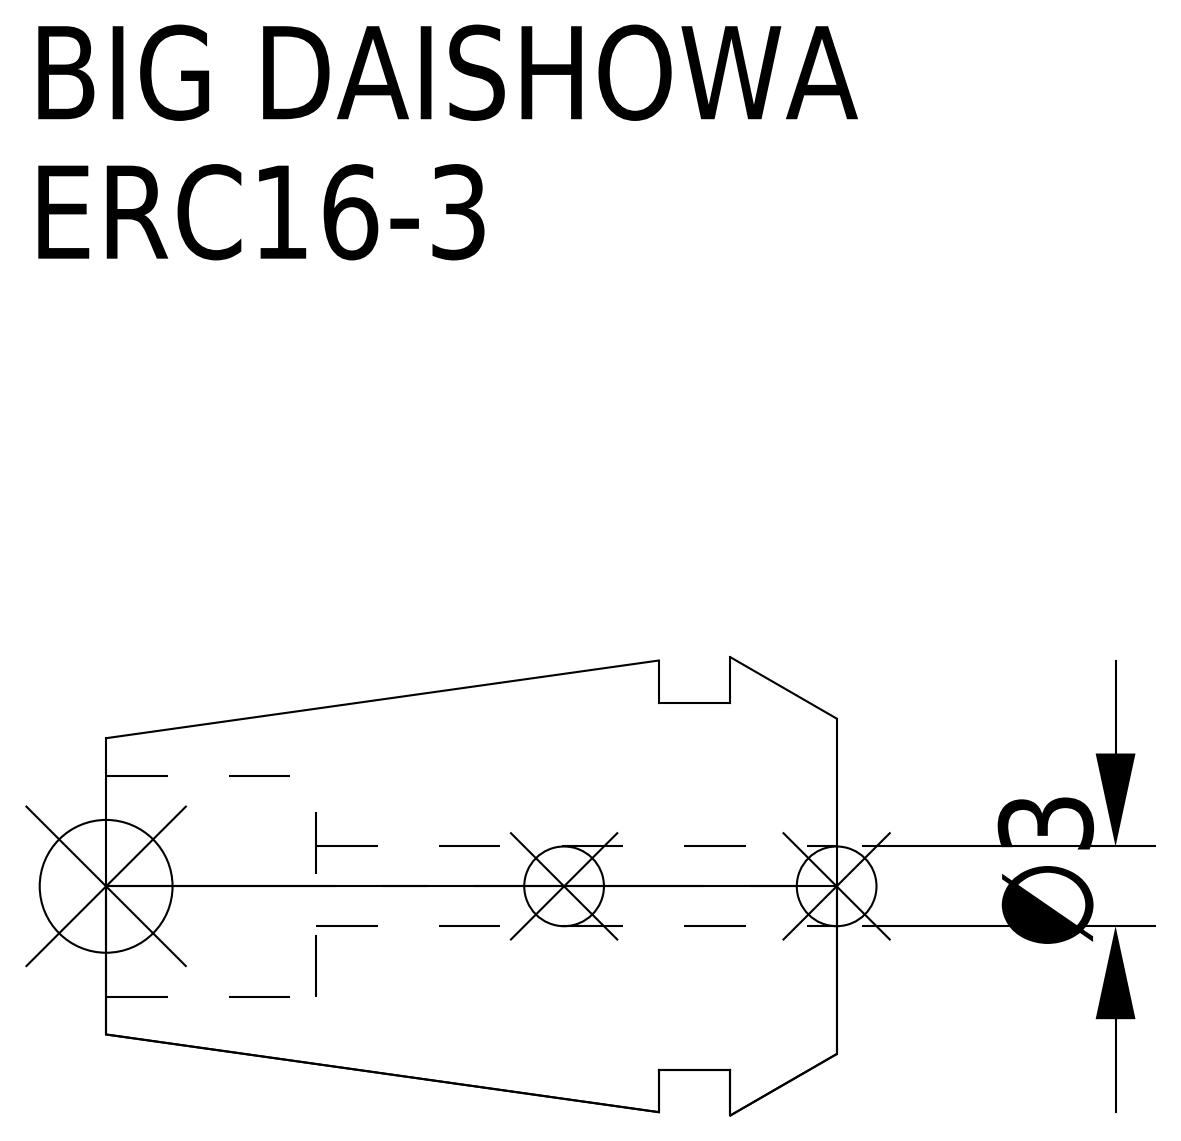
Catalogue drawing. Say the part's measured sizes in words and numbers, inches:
The part is named "ERC16-3". Its 3-D file was written by "CREO PARAMETRIC BY PTC INC, 2016380 (AUTOMOTIVE_DESIGN)". It is 1 solid with 15 faces: 5 planar, 6 cylindrical and 4 other. Overall it measures 1.083 by 0.679 by 0.679 inches. Its volume is 0.234 cubic inches and its surface area 3.137 square inches. Round holes: 1 of diameter 0.118, 1 of diameter 0.327. Round bosses or shafts: 1 of diameter 0.543. The main face-to-face distances are 0.157, 0.264, 0.106, 0.771, 0.614, 0.507, 1.083, 0.925, 0.819, 0.311.
